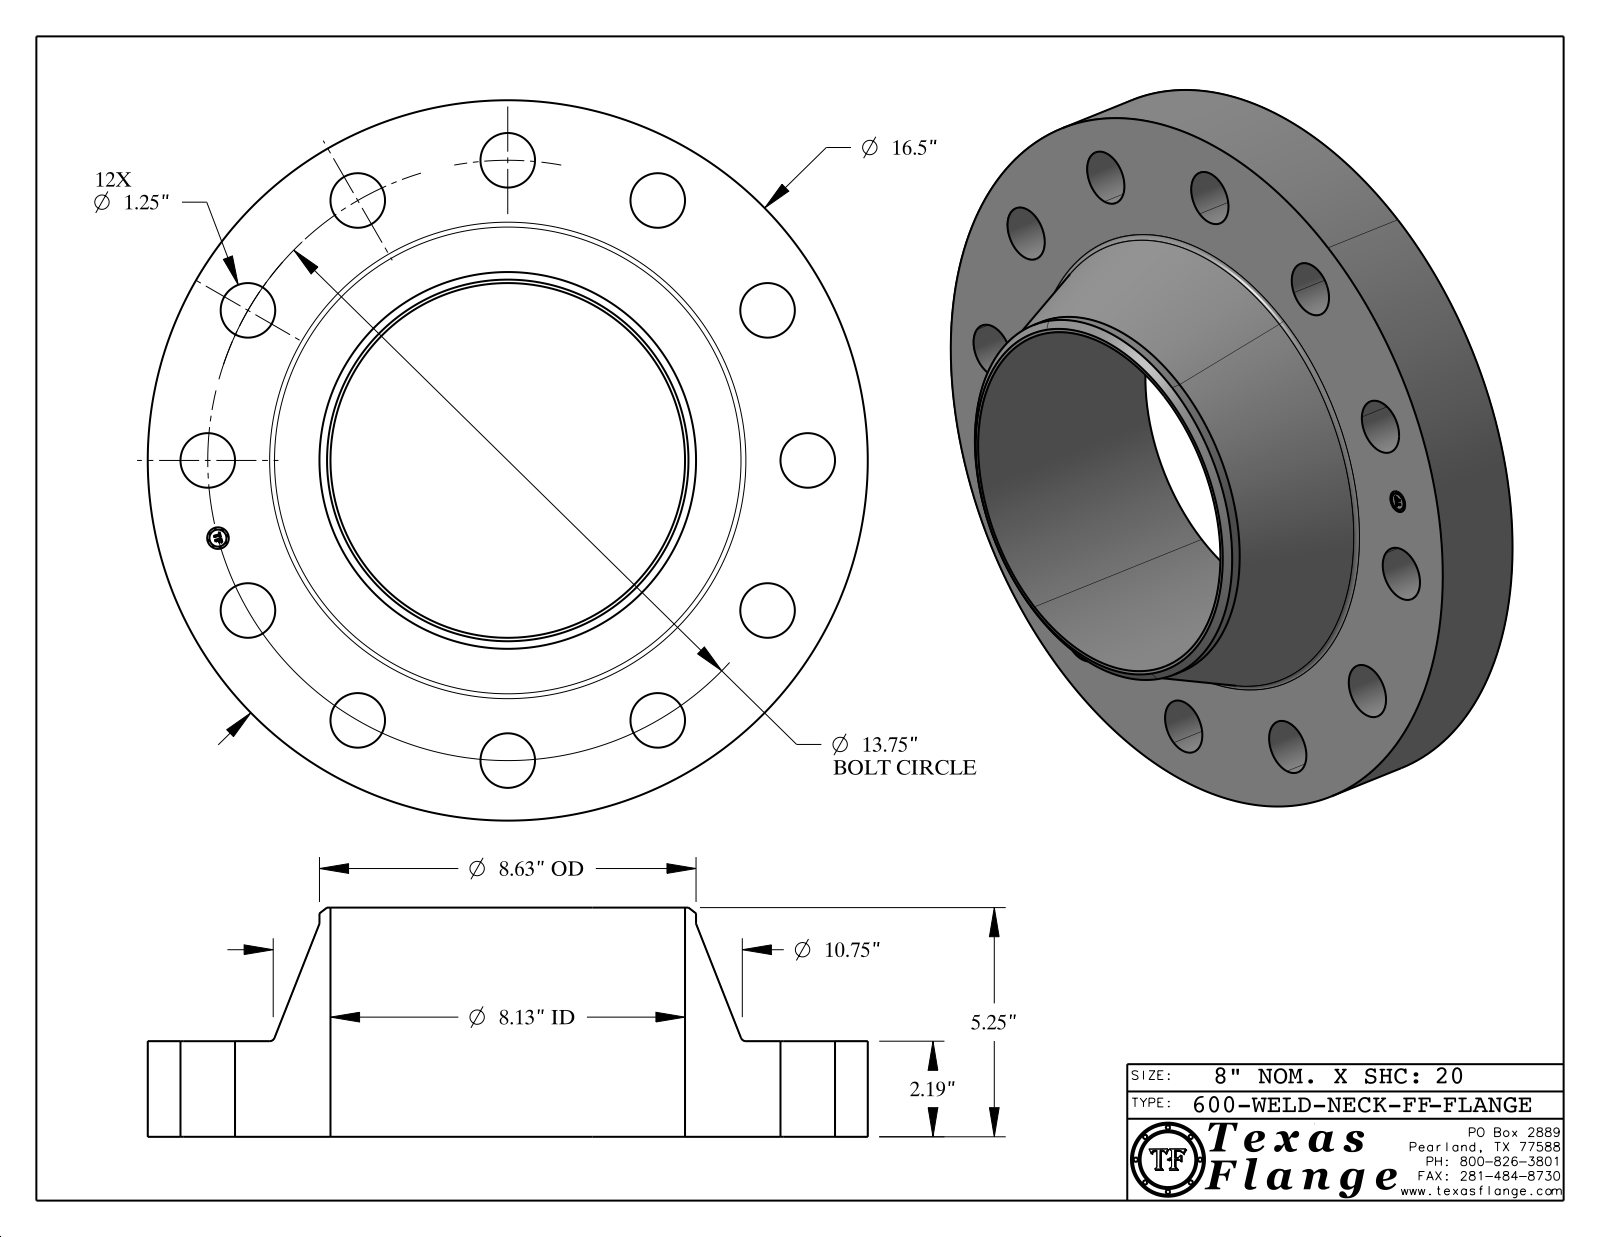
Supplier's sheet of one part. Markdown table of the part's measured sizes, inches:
| quantity | value |
| --- | --- |
| part name | 600-WELD-NECK-FF |
| STEP written by | CATIA V5 STEP AP214 (AUTOMOTIVE_DESIGN) |
| units | inches |
| bodies | 1 solid, 424 faces (368 planar, 50 cylindrical, 6 other) |
| overall size | 16.5 × 16.5 × 5.25 |
| volume | 384.4 in³ |
| surface area | 708 in² |
| round holes (diameter × count) | 1.25 × 12, 0.495 × 1, 8.125 × 1 |
| round bosses / shafts (diameter × count) | 0.03 × 8, 16.5 × 1, 8.63 × 1, 0.39 × 1 |
| main face-to-face distances | 2.19, 5.25, 3.06, 2.175, 0.015, 3.075, 0.148, 0.145, 0.027, 0.096 |
| hole center spacings | 6.875, 6.875, 9.723, 11.908, 13.281, 3.559, 3.559, 13.75 |
